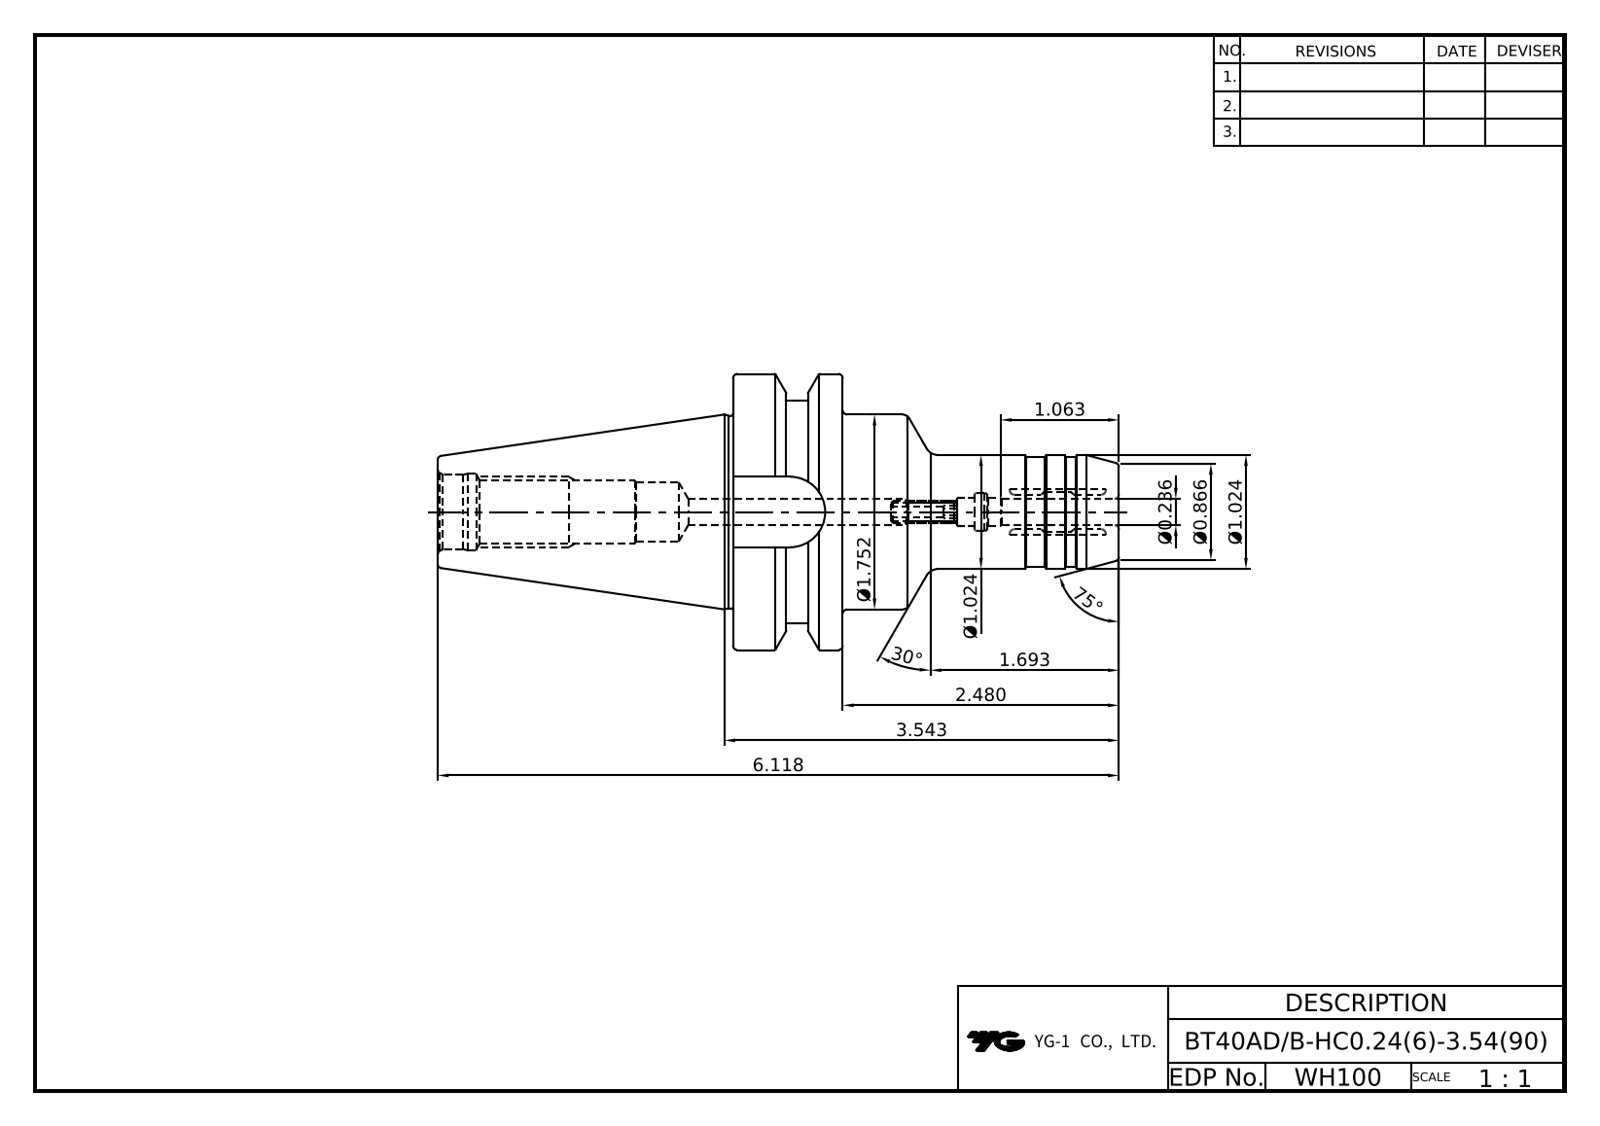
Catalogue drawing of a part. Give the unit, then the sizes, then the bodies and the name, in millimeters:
Units: millimetres
Overall size (bounding box): 155.4 × 63 × 63
Round holes (diameter × count): ⌀3.24 ×4, ⌀4 ×4, ⌀4.3 ×1, ⌀6 ×1, ⌀6.6 ×1, ⌀13.5 ×1, ⌀13.84 ×1, ⌀17 ×1, ⌀17.6 ×1
Round bosses / shafts (diameter × count): ⌀63 ×1, ⌀51 ×1, ⌀44.5 ×1, ⌀44 ×1, ⌀26 ×1, ⌀25 ×1
Partial cylindrical surfaces — rounded edges, fillets, slot ends (radius × count): R8.05 ×1
Main face-to-face distances: 25, 45.2, 88, 63, 17.1, 7.9, 70.9, 12.1, 5, 12.9
Volume: 171 213 mm³ · Surface area: 29 366 mm²
Bodies: 1 solid, 90 faces (21 planar, 34 cylindrical, 35 other)
Part name (STEP PRODUCT): LO-BT40ADB-HC6-90
STEP written by: Autodesk Inventor 2022 (AUTOMOTIVE_DESIGN)
